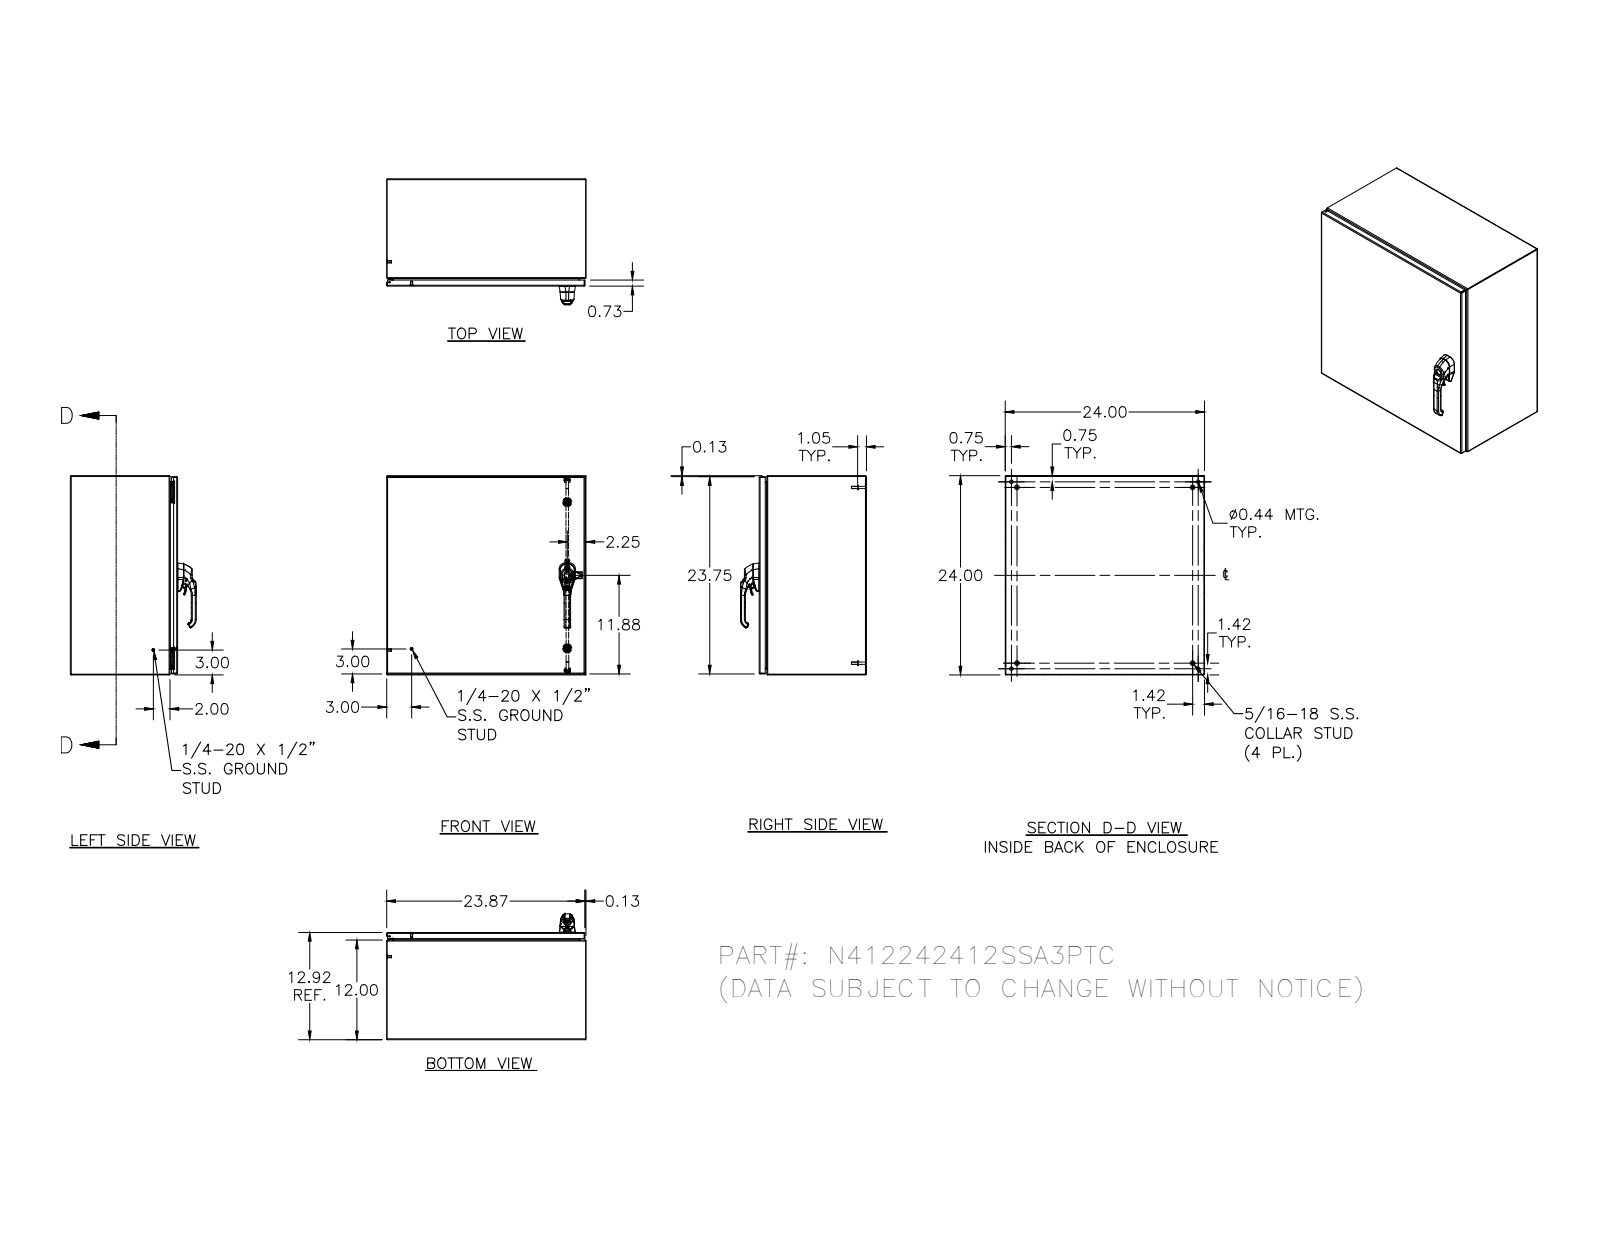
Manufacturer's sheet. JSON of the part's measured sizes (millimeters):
{"part_name": "N412242412SSA3PTC; N412242412SSA3PTCBKP; N4122424SSA3PTCLID; HFW328176 (+8 more)", "step_written_by": "Autodesk Inventor 2011 (AUTOMOTIVE_DESIGN)", "units": "millimeters", "bodies": {"solids": 63, "faces": 3088, "planar": 1046, "cylindrical": 1119, "other": 923}, "overall_size": [609.6, 609.6, 385.2], "volume_mm3": 3197000, "surface_area_mm2": 3325000, "round_holes": [[4.2, 5], [4.8, 5], [2.4, 4], [3.9, 4], [4.2, 4], [4.4, 4], [5, 4], [11.1, 4], [5.4, 3], [2.7, 2], [4, 2], [4.1, 2]], "round_bosses_or_shafts": [[6.4, 10], [6, 6], [15, 5], [14.3, 4], [9.1, 4], [8.1, 4], [7.9, 4], [7.6, 4]], "partial_cylinders_radius": [[0.5, 180], [0.3, 101], [0.8, 30], [1.3, 26], [3, 23], [0.5, 21], [2.7, 20], [0.4, 18]], "face_to_face_distances": [1.9, 607.7, 326.2, 605.8, 609.6, 328.1, 324.3, 302.9, 23.3, 18.8], "hole_center_spacings": [507.9, 571.5, 580.9, 0.4, 16.8, 41.1, 524.7, 594.8]}
